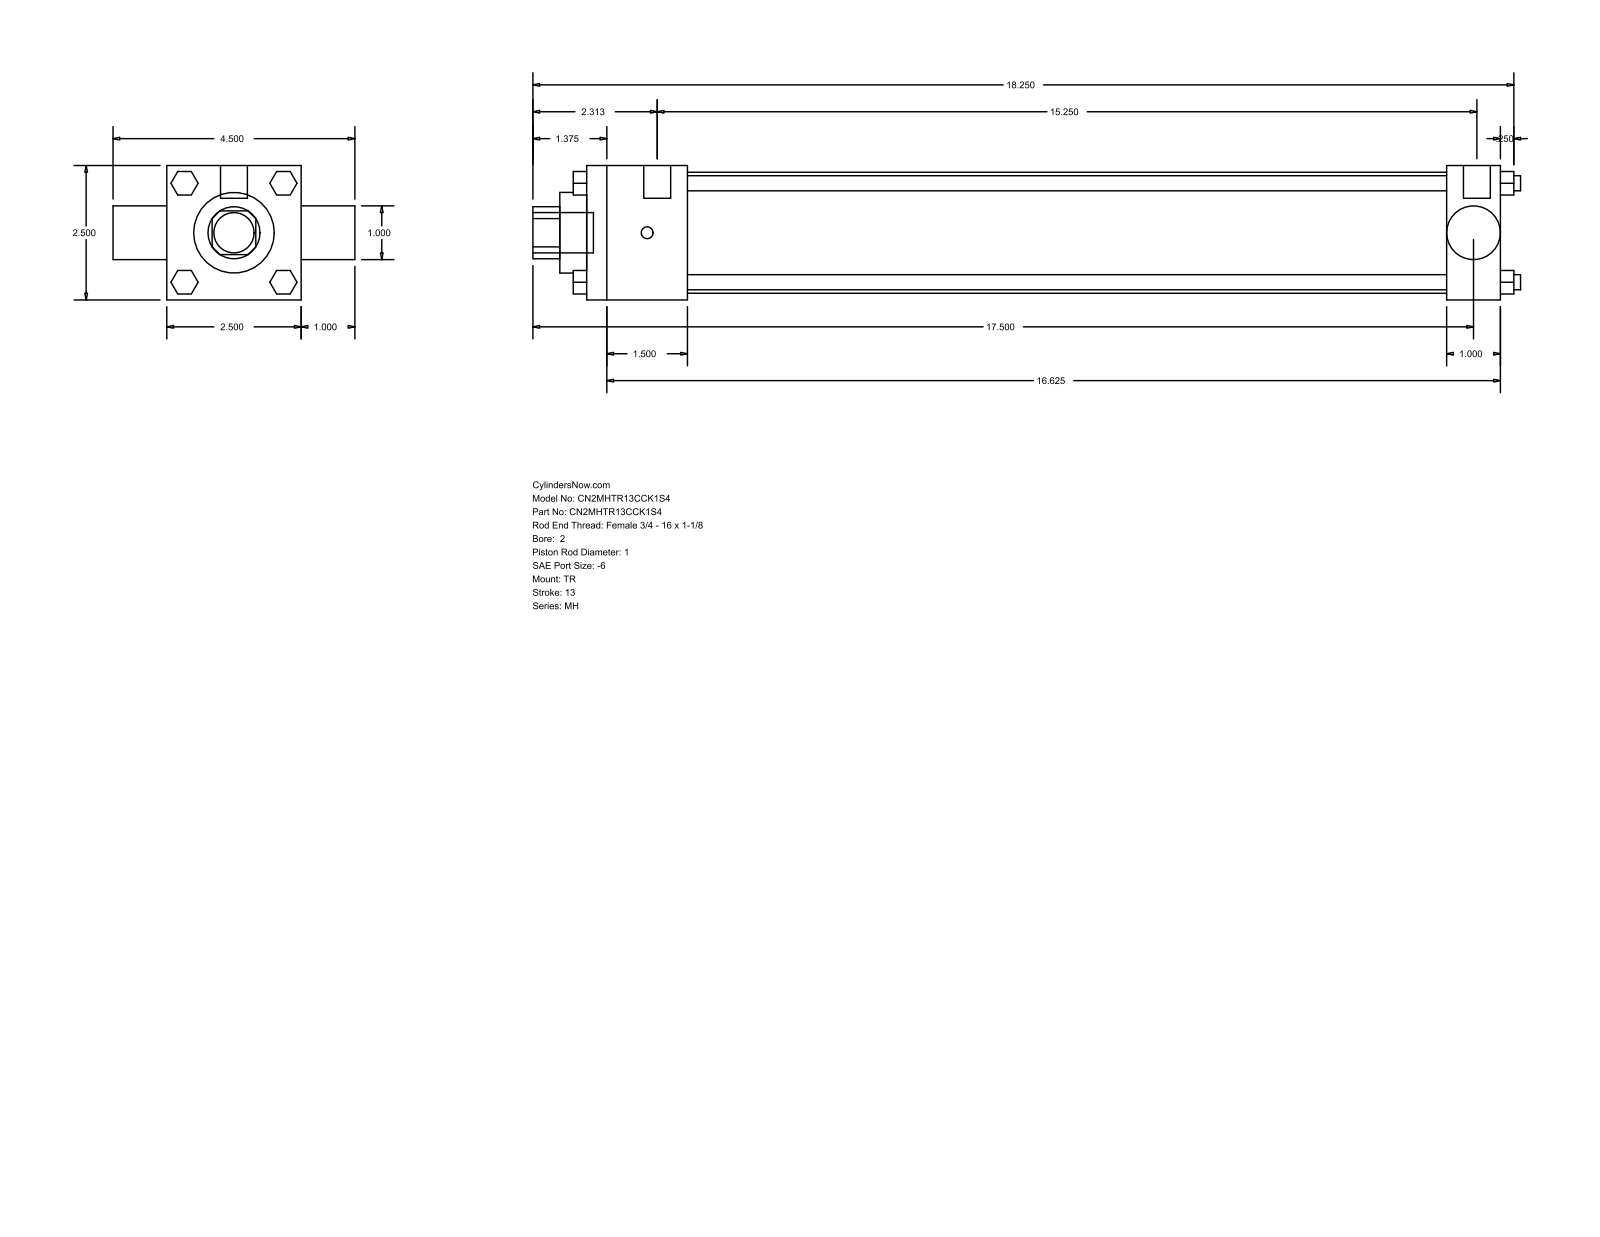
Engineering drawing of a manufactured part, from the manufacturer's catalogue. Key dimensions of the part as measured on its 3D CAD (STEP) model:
Part name (STEP PRODUCT): MH_TR__0200_1
STEP written by: GSSL Pune (CONFIG_CONTROL_DESIGN)
Units: millimetres
Bodies: 0 solids, 120 faces (92 planar, 28 cylindrical, 0 other)
Overall size (bounding box): 466.73 × 114.3 × 63.5
Round holes (diameter × count): ⌀25.35 ×1, ⌀25.4 ×1, ⌀38.1 ×1, ⌀57.15 ×1
Round bosses / shafts (diameter × count): ⌀7.14 ×4, ⌀5.56 ×3, ⌀12.7 ×2, ⌀19.05 ×1
Partial cylindrical surfaces — rounded edges, fillets, slot ends (radius × count): R12.29 ×1
Main face-to-face distances: 63.5, 431.8, 25.4, 47.63, 406.4, 358.77, 384.17, 88.9, 444.5, 6.35
